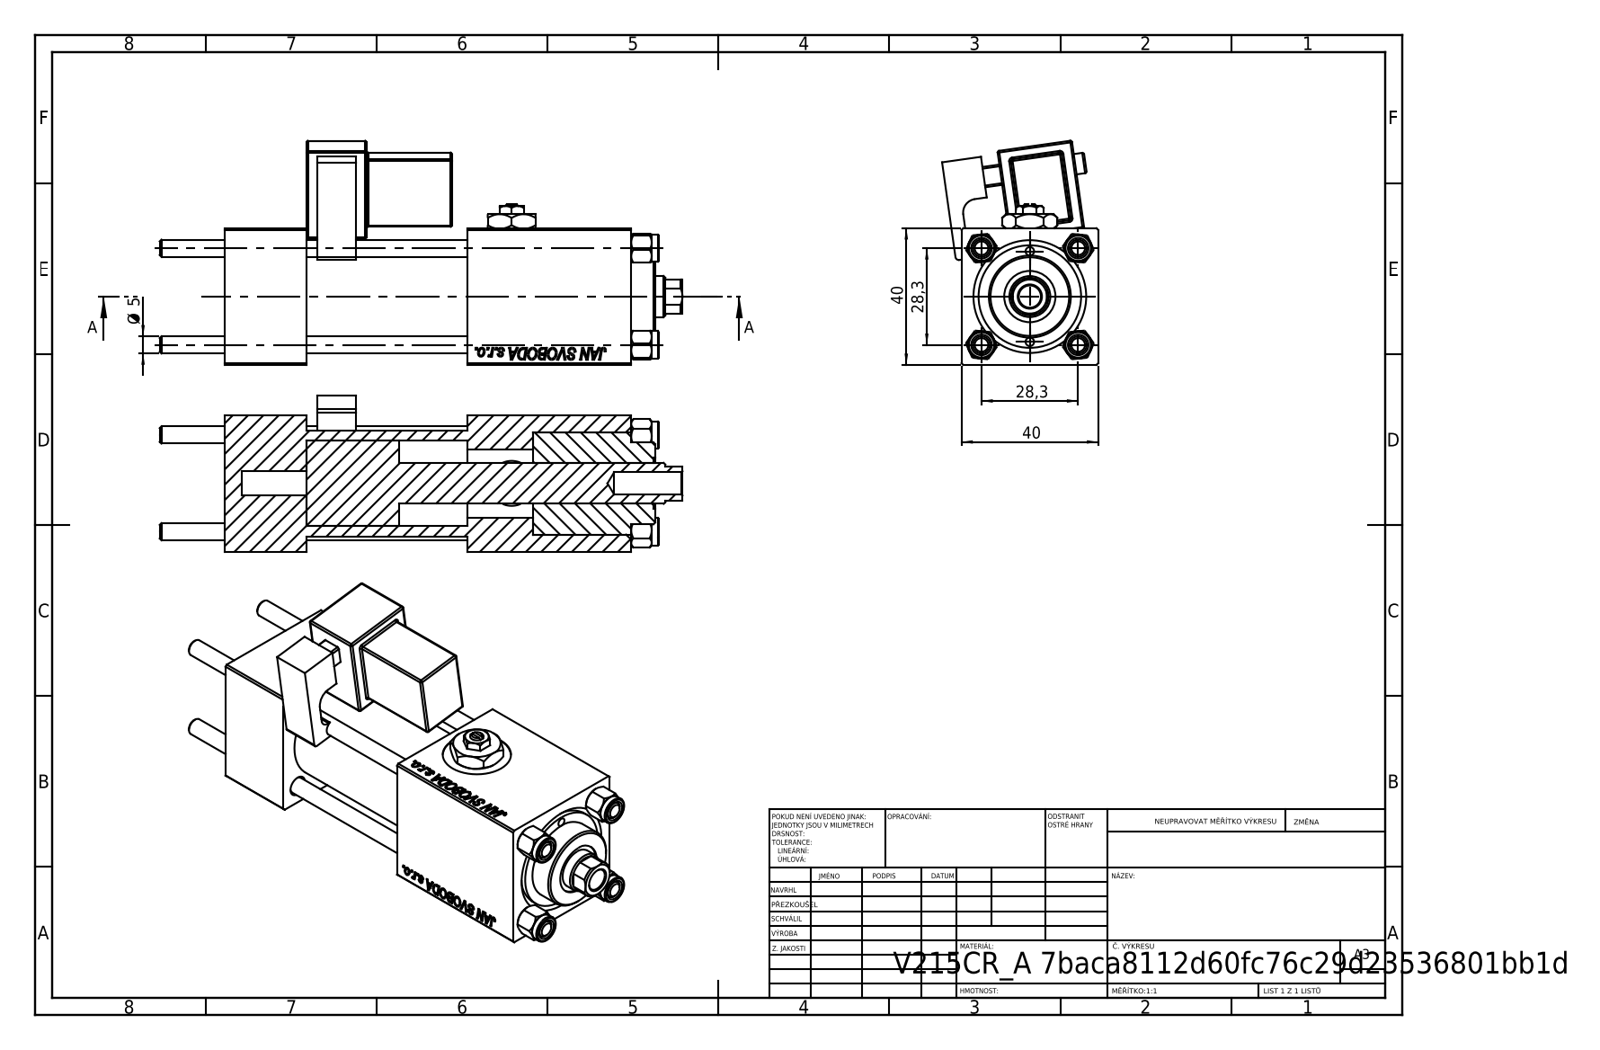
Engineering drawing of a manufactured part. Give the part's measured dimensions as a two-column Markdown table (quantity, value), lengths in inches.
| quantity | value |
| --- | --- |
| part name | CR025_012_A_0_G_A_G_M_020_+#_##_TYCINKA; V215_VC_A; Zatka_pro_OIL_PORT; NUT_M5 (+3 more) |
| STEP written by | SolidWorks 2019 (CONFIG_CONTROL_DESIGN) |
| units | inches |
| bodies | 13 solids, 1264 faces (574 planar, 116 cylindrical, 574 other) |
| overall size | 6.024 × 2.582 × 1.799 |
| volume | 10.03 in³ |
| surface area | 101.8 in² |
| round holes (diameter × count) | 0.197 × 4, 0.787 × 3, 0.098 × 2, 0.276 × 2, 0.518 × 2, 0.256 × 1, 0.472 × 1, 0.591 × 1, 0.984 × 1, 1.181 × 1 |
| round bosses / shafts (diameter × count) | 0.315 × 4, 1.22 × 1, 0.945 × 1, 0.236 × 1 |
| partial cylindrical surfaces (radius × count) | 0.02 × 24, 0.039 × 1, 0.098 × 1, 0.157 × 1, 0.217 × 1 |
| main face-to-face distances | 1.575, 0.945, 0.118, 4.685, 3.74, 3.555, 2.61, 1.13, 1.85, 2.795 |
| hole center spacings | 0.558, 0.788, 1.114, 1.214, 0.522, 1.576, 1.043, 2.835 |
